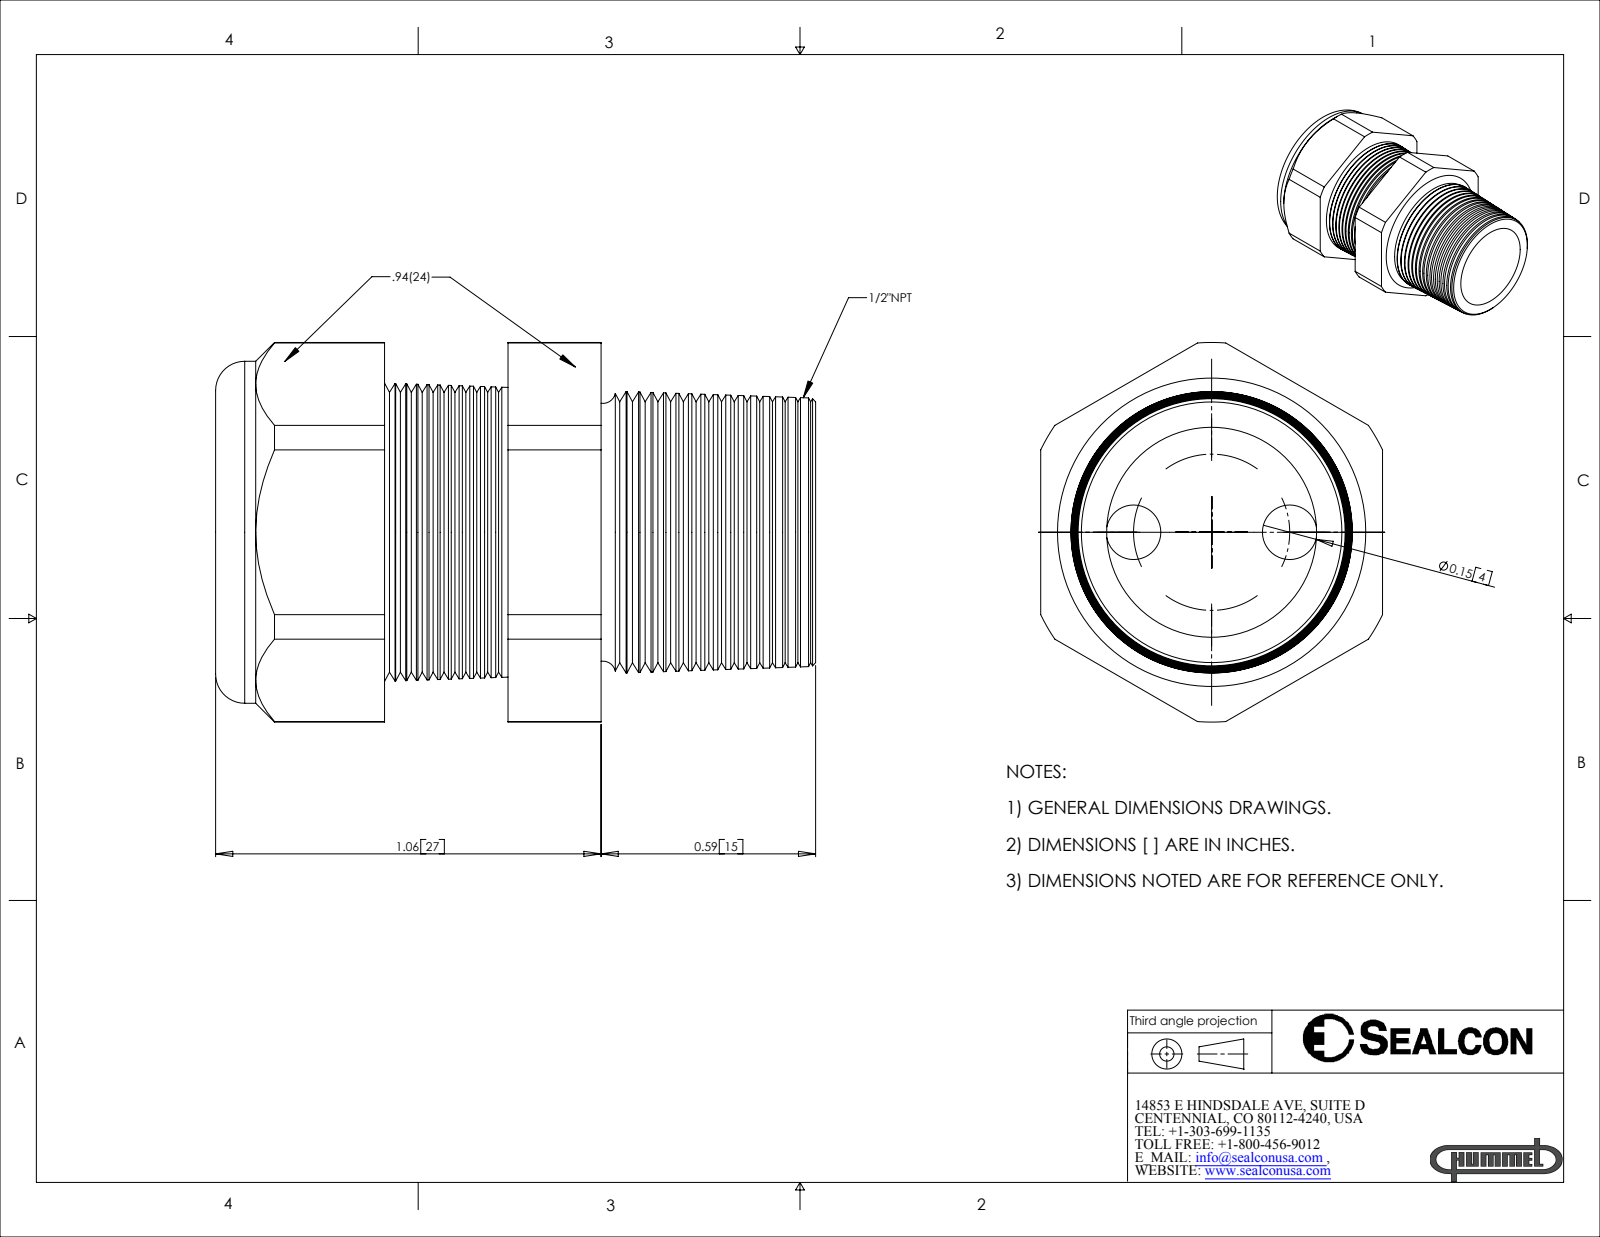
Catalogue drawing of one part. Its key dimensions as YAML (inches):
part_name: "CD13N7-GY"
step_written_by: "SolidWorks 2007 (CONFIG_CONTROL_DESIGN)"
units: inches
bodies: {solids: 2, faces: 208, planar: 20, cylindrical: 24, other: 164}
overall_size: [1.57, 1.043, 0.94]
volume: 0.567
surface_area: 11.56
round_holes:
  - {diameter: 0.15, count: 2}
  - {diameter: 0.58, count: 1}
  - {diameter: 0.6, count: 1}
round_bosses_or_shafts:
  - {diameter: 0.94, count: 1}
partial_cylinders:
  - {radius: 0.522, count: 1}
face_to_face_distances: [0.94, 0.454, 0.115, 0.34, 0.33, 0.444, 0.784, 0.02, 0.35, 0.465]
hole_center_spacings: [0.215, 0.429]
